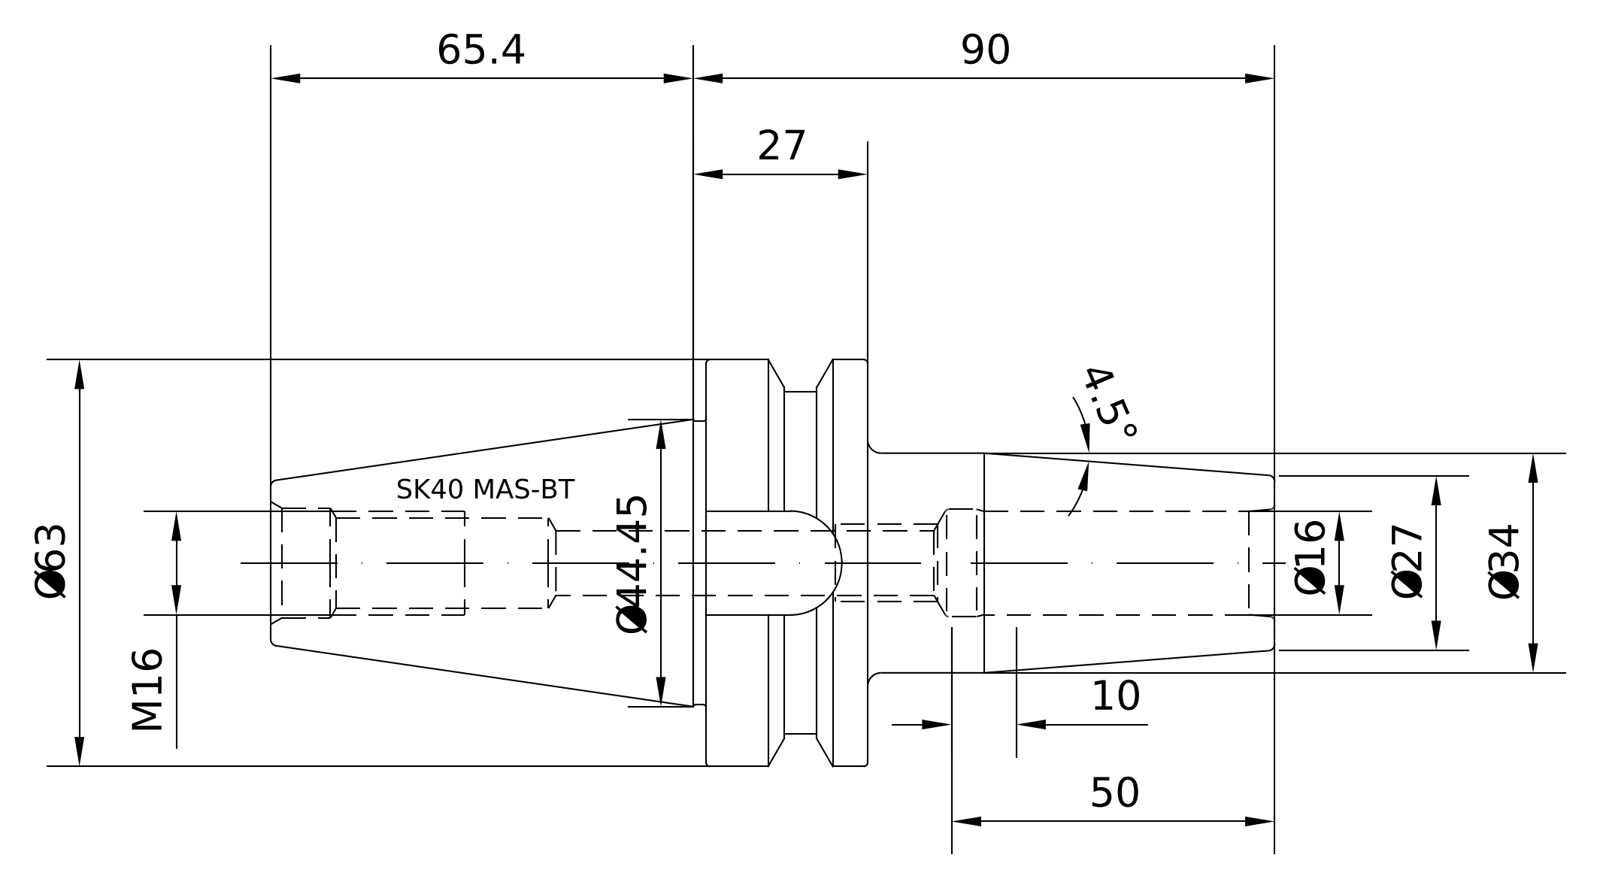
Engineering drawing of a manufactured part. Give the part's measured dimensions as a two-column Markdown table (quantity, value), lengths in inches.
| quantity | value |
| --- | --- |
| part name | 40-640-16 |
| STEP written by | PRO/ENGINEER BY PARAMETRIC TECHNOLOGY CORPORATION, 2010430 (CONFIG_CONTROL_DESIGN) |
| units | inches |
| bodies | 1 solid, 96 faces (26 planar, 22 cylindrical, 48 other) |
| overall size | 6.118 × 2.48 × 2.48 |
| volume | 10.11 in³ |
| surface area | 46.72 in² |
| round holes (diameter × count) | 0.545 × 1, 0.63 × 1, 0.67 × 1, 0.689 × 1 |
| round bosses / shafts (diameter × count) | 2.48 × 1, 2.077 × 1, 1.722 × 1, 1.339 × 1, 0.63 × 1 |
| partial cylindrical surfaces (radius × count) | 0.319 × 1 |
| main face-to-face distances | 0.984, 1.768, 3.465, 2.48, 1.496, 0.512, 1.969, 0.638, 2.654, 3.638 |
